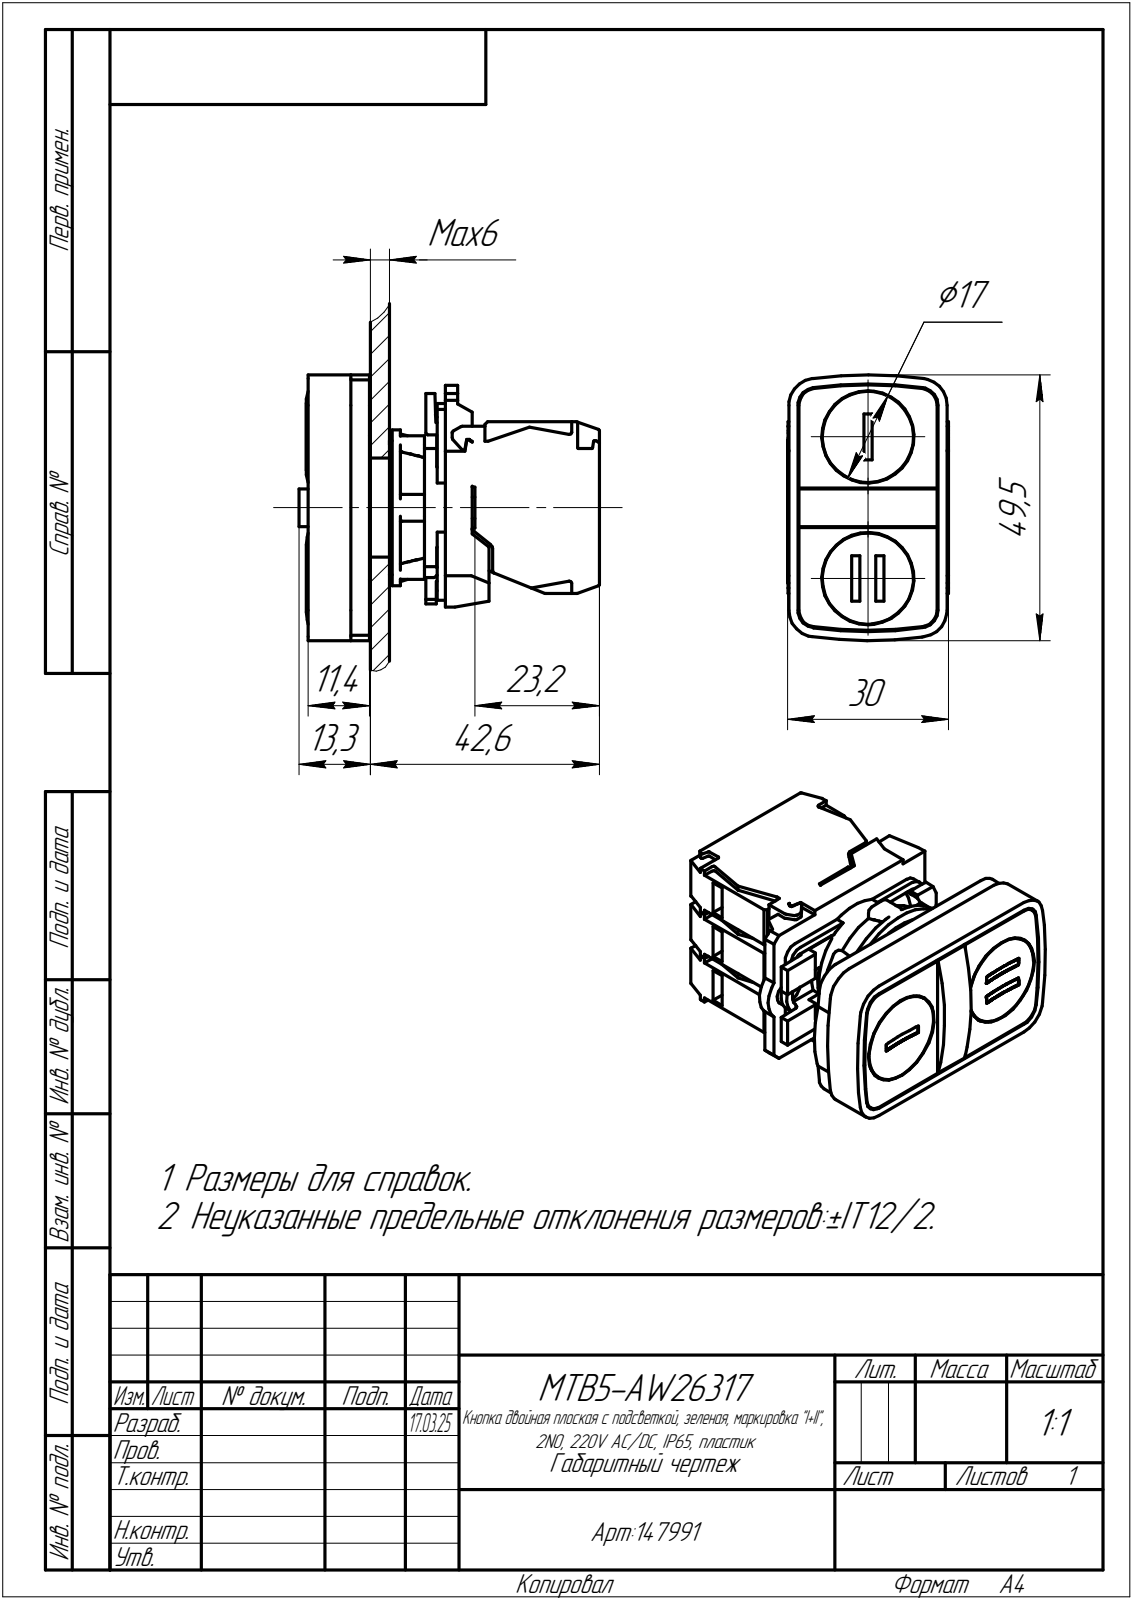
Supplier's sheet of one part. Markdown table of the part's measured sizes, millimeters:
| quantity | value |
| --- | --- |
| part name | MTB5-AW26317 |
| STEP written by | C3D Toolkit (CONFIG_CONTROL_DESIGN) |
| units | millimeters |
| bodies | 1 solid, 649 faces (455 planar, 177 cylindrical, 17 other) |
| overall size | 55.9 × 49.5 × 30 |
| volume | 47 662 mm³ |
| surface area | 19 523 mm² |
| round holes (diameter × count) | 6 × 2, 17.2 × 2, 5.2 × 1, 20.5 × 1 |
| round bosses / shafts (diameter × count) | 17 × 2, 29 × 1, 26.8 × 1, 25 × 1, 22 × 1 |
| partial cylindrical surfaces (radius × count) | 1 × 15, 0.2 × 13, 0.5 × 7, 2.5 × 4, 3.1 × 4, 3.3 × 4, 4.35 × 4, 5 × 4 |
| main face-to-face distances | 10, 9.9, 20, 19.9, 10.1, 14.1, 9, 25.5, 11.4, 19.1 |
| hole center spacings | 4.7, 8.5, 13.2, 21.7, 17, 26.4 |
